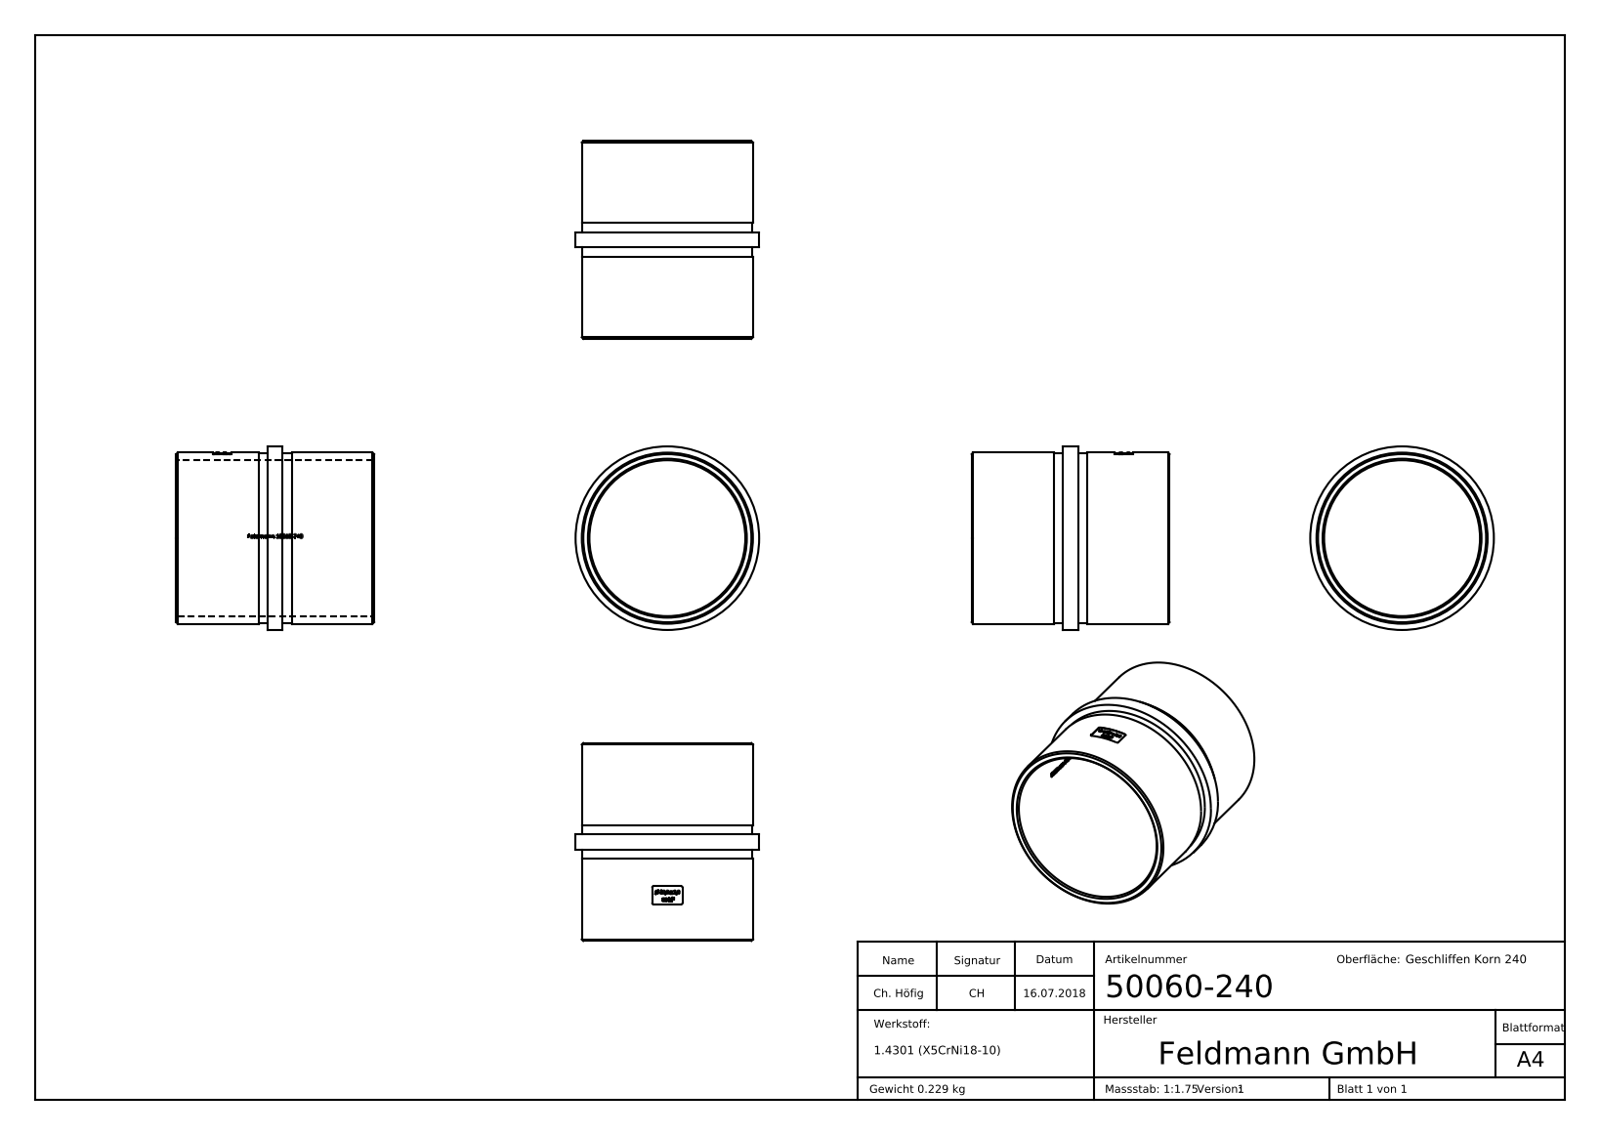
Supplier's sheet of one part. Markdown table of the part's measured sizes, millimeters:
| quantity | value |
| --- | --- |
| part name | 50060-240 |
| STEP written by | SolidWorks 2015 (CONFIG_CONTROL_DESIGN) |
| units | millimeters |
| bodies | 1 solid, 432 faces (164 planar, 69 cylindrical, 199 other) |
| overall size | 65 × 60.3 × 60.3 |
| volume | 28 987 mm³ |
| surface area | 23 544 mm² |
| round holes (diameter × count) | 51.2 × 1 |
| round bosses / shafts (diameter × count) | 60.3 × 1, 56.2 × 1, 55.8 × 1 |
| partial cylindrical surfaces (radius × count) | 0.5 × 4, 25.7 × 1, 28 × 1 |
| main face-to-face distances | 30, 35, 5, 65, 27, 38, 3, 8, 11, 12 |
